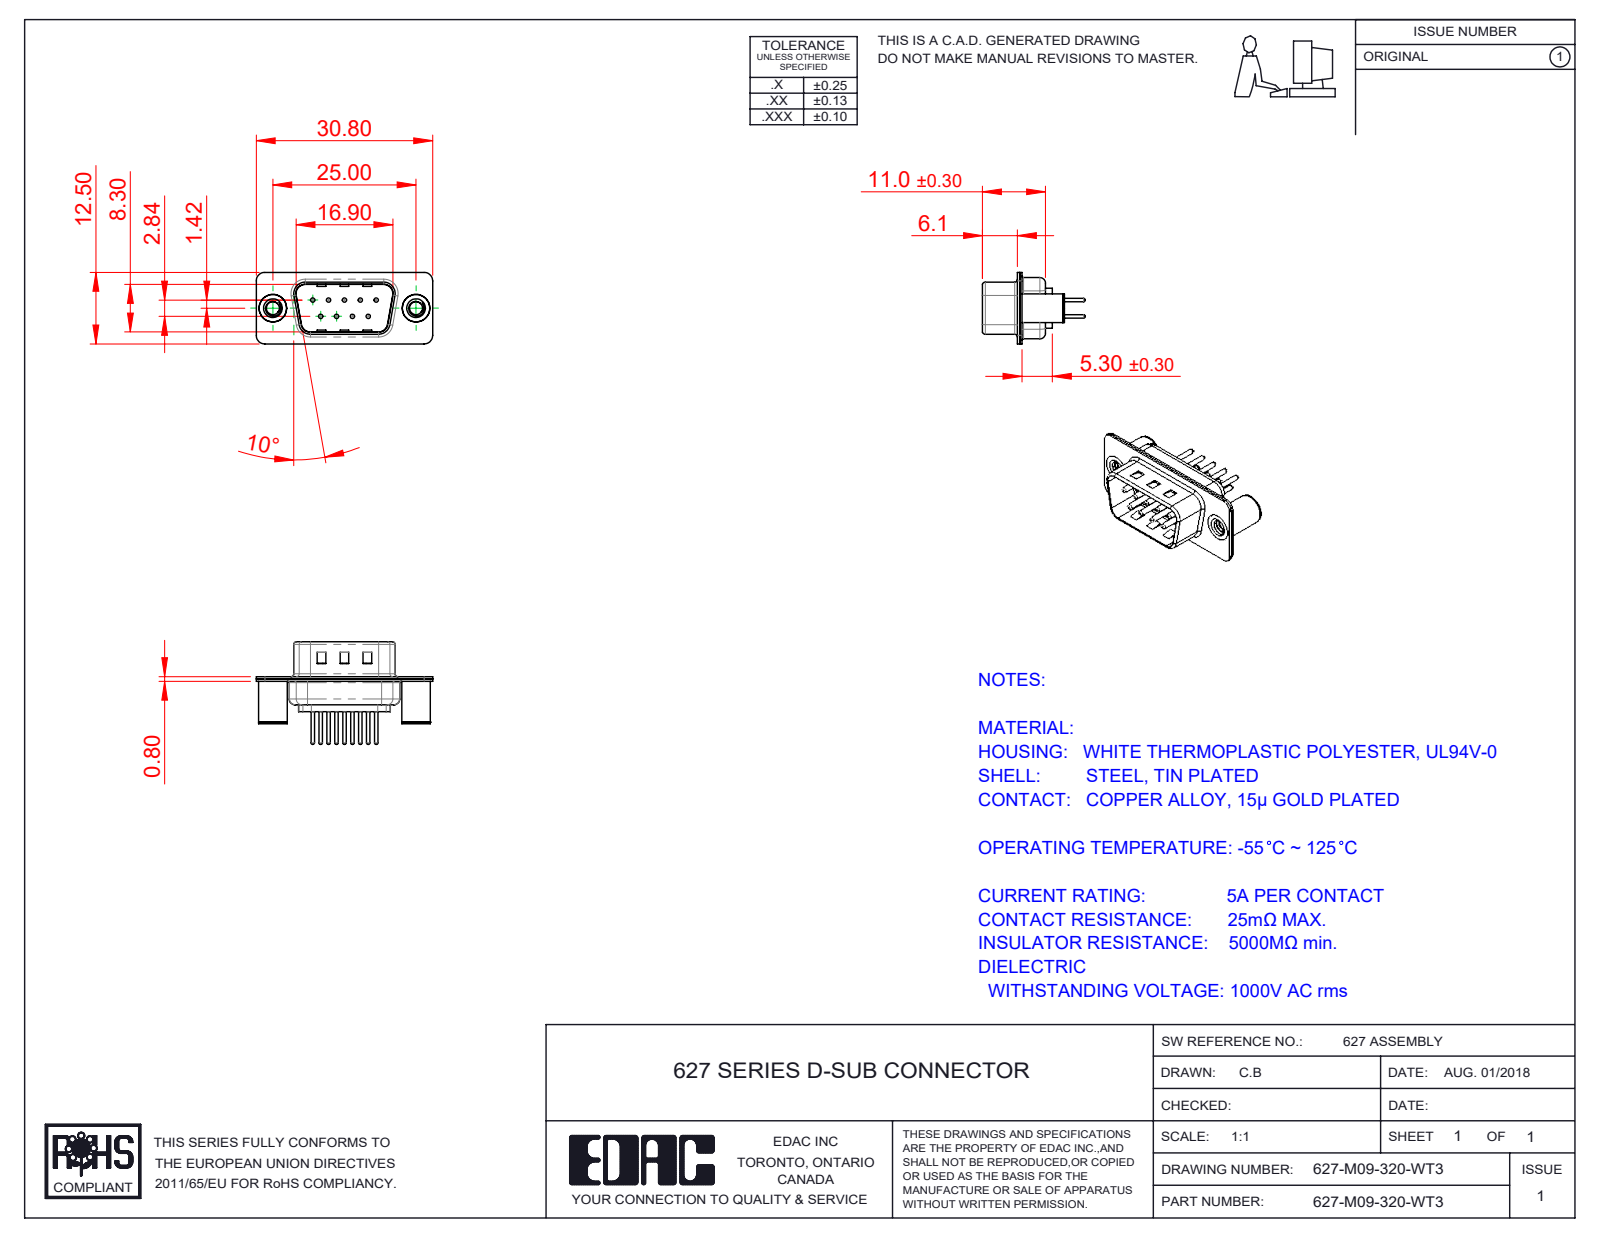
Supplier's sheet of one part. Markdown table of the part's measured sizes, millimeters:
| quantity | value |
| --- | --- |
| part name | 627M Shell Rear_09 Contacts; 627M Contact Row 1_20; 627M Housing_09 Contacts; 627M 4-40 Threaded Board Spacer (+3 more) |
| STEP written by | SolidWorks 2020 (CONFIG_CONTROL_DESIGN) |
| units | millimeters |
| bodies | 14 solids, 671 faces (170 planar, 279 cylindrical, 222 other) |
| overall size | 30.8 × 17.9 × 12.5 |
| volume | 1 433 mm³ |
| surface area | 3 832 mm² |
| round holes (diameter × count) | 0.75 × 9, 1.6 × 9, 2 × 9, 2.26 × 2, 3.26 × 2, 4 × 2, 4.8 × 2 |
| round bosses / shafts (diameter × count) | 1.5 × 9, 0.6 × 9, 5 × 2, 4.9 × 2 |
| partial cylindrical surfaces (radius × count) | 1.5 × 16, 2 × 12, 0.5 × 8, 1.6 × 8, 0.25 × 4, 0.6 × 4, 0.65 × 4, 0.9 × 4 |
| main face-to-face distances | 0.4, 0.8, 9.5, 9.1, 8.7, 0.65, 9.9, 1.2, 5.3, 6.1 |
| hole center spacings | 3.16, 2.77, 5.54, 5.03, 5.04, 8.31, 7.1, 7.48 |
